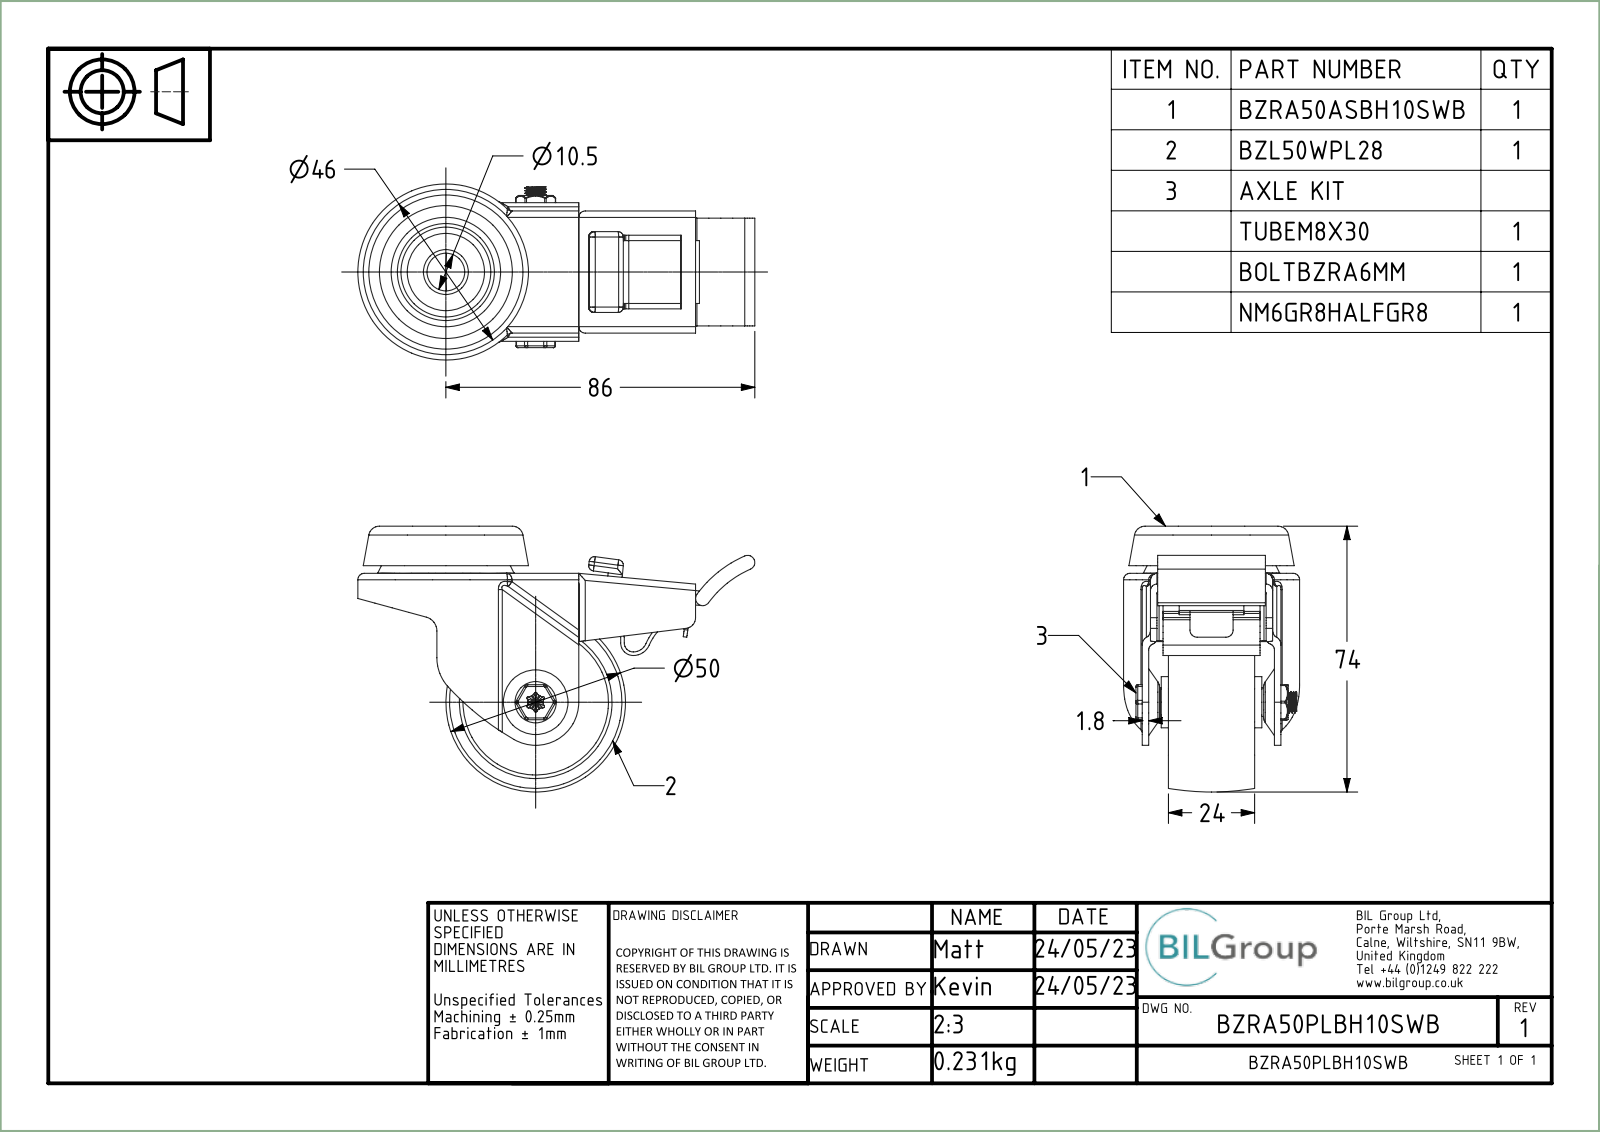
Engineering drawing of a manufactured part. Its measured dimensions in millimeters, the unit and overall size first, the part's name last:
Units: millimetres
Overall size (bounding box): 110.5 × 74 × 49
Round holes (diameter × count): ⌀6 ×1, ⌀6.2 ×1, ⌀6.3 ×1, ⌀8.1 ×1, ⌀8.2 ×1, ⌀10.5 ×1, ⌀10.56 ×1, ⌀42.5 ×1
Round bosses / shafts (diameter × count): ⌀39 ×1, ⌀38 ×1, ⌀18 ×1, ⌀14.76 ×1, ⌀14.25 ×1, ⌀8 ×1, ⌀7.95 ×1, ⌀5 ×1
Partial cylindrical surfaces — rounded edges, fillets, slot ends (radius × count): R1 ×28, R1.8 ×22, R0.5 ×12, R0.9 ×12, R1.5 ×11, R0.4 ×6, R2 ×6, R3 ×3
Main face-to-face distances: 1.8, 1.81, 4, 3.2, 30.4, 1, 32.2, 5, 13.2, 17.2
Volume: 52 158 mm³ · Surface area: 48 641 mm²
Bodies: 9 solids, 591 faces (137 planar, 286 cylindrical, 168 other)
Part name (STEP PRODUCT): BZRA50ASBH10SWB; ZINC PLATED PRESSED STEEL FORKS; ZINC PLATED PRESSED STEEL HEAD; ZINC PLATED PRESSED STEEL BRAKE (+8 more)
STEP written by: Spatial InterOp 3D (CONFIG_CONTROL_DESIGN)
